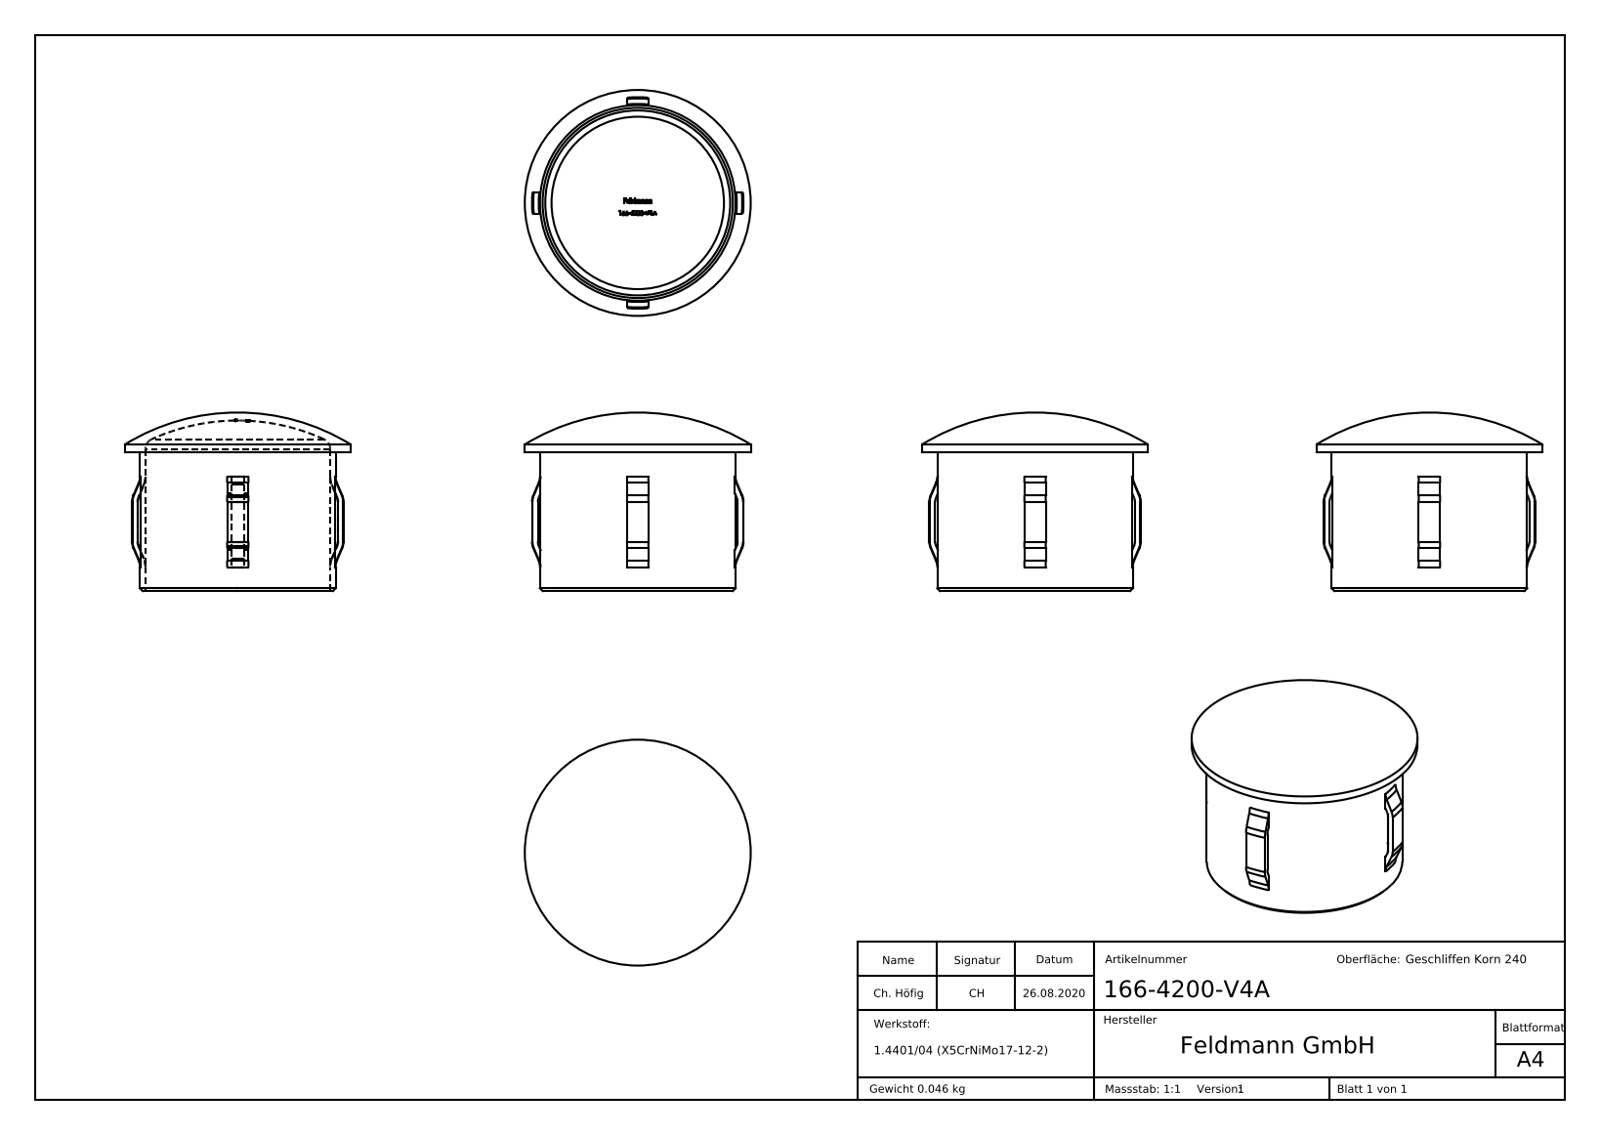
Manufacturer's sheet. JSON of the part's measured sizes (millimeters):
{"part_name": "166-4200-V4A", "step_written_by": "SolidWorks 2018 (CONFIG_CONTROL_DESIGN)", "units": "millimeters", "bodies": {"solids": 1, "faces": 355, "planar": 142, "cylindrical": 16, "other": 197}, "overall_size": [42.4, 42.4, 33.5], "volume_mm3": 5704, "surface_area_mm2": 9531, "round_holes": [[34.7, 1]], "round_bosses_or_shafts": [[42.4, 1], [36.7, 1]], "partial_cylinders_radius": [[18.85, 1], [19.85, 1]], "face_to_face_distances": [0.75, 3.25, 26, 4, 2.5, 1.25, 1.97, 0.76, 0.83, 2.33]}
